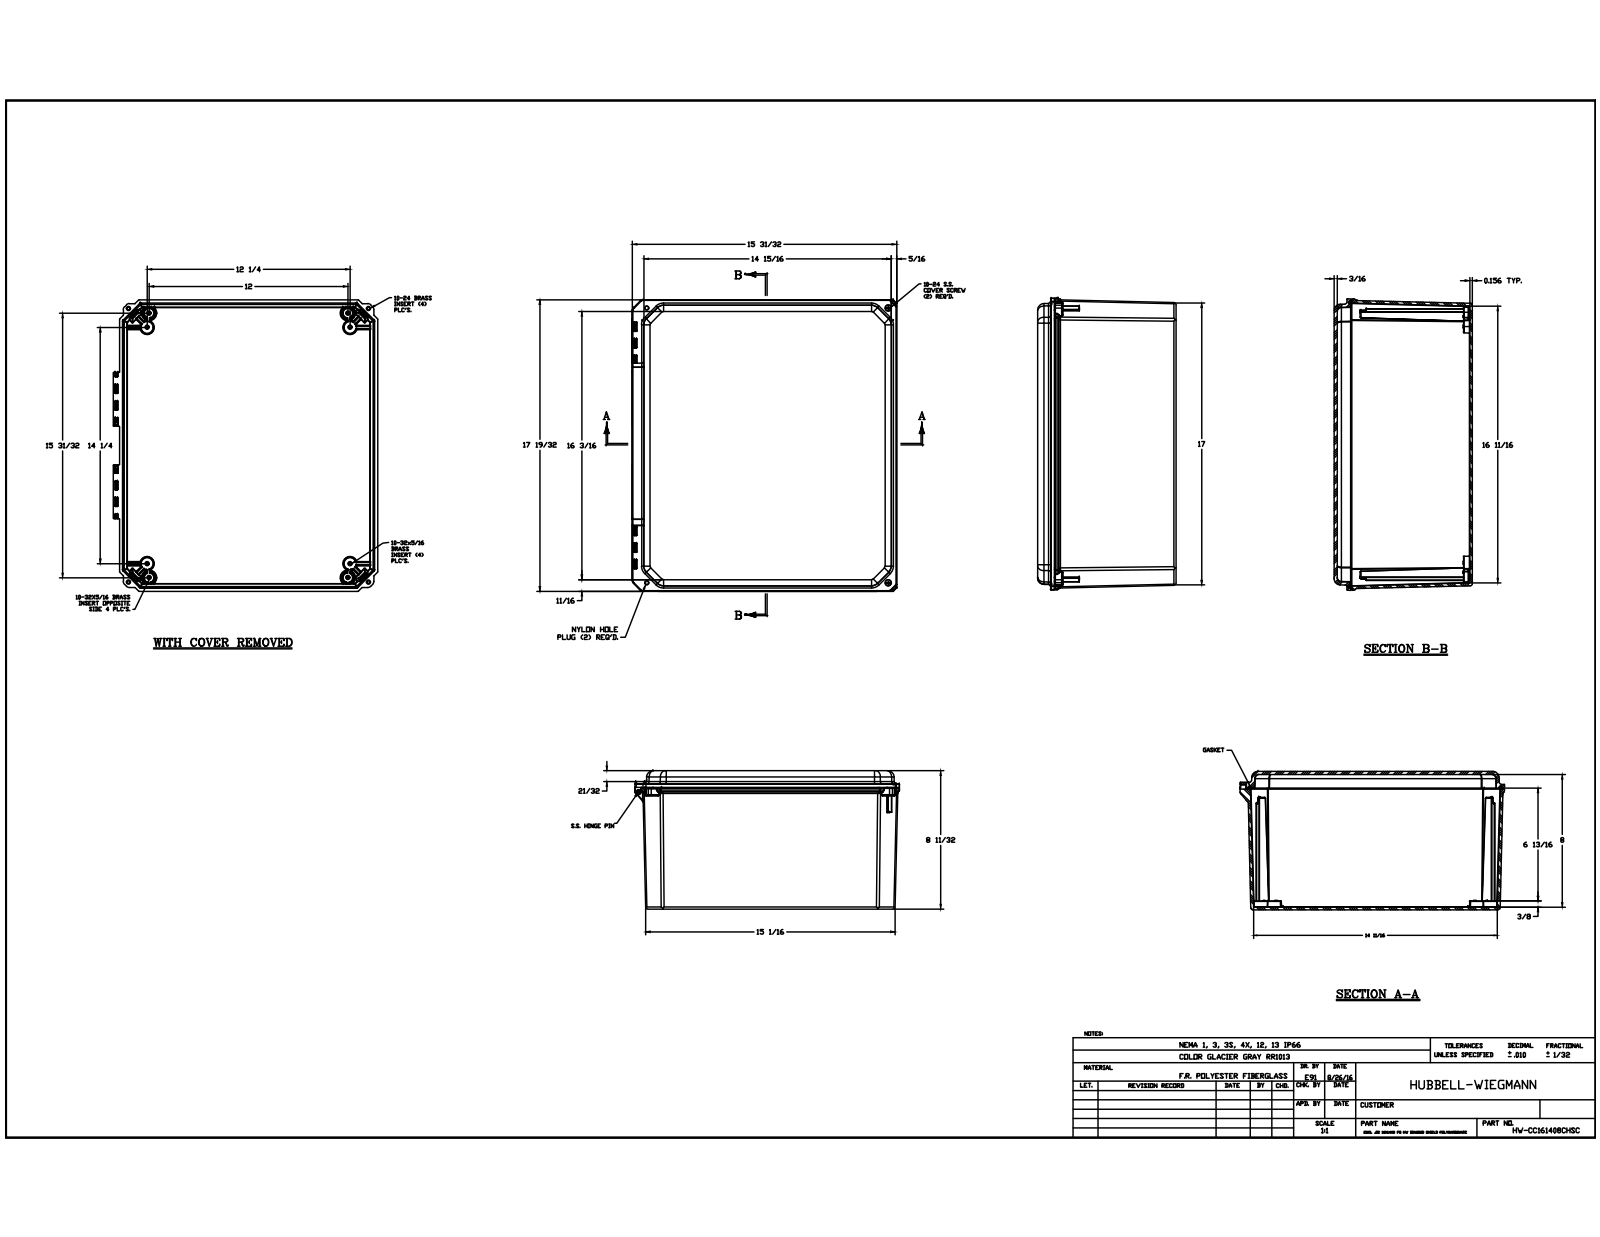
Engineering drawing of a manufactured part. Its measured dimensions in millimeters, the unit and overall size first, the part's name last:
Units: millimetres
Overall size (bounding box): 446.8 × 405.5 × 211.87
Round holes (diameter × count): ⌀3.96 ×12, ⌀3.86 ×8, ⌀5.56 ×4, ⌀6.4 ×4, ⌀7.92 ×4, ⌀3.48 ×2, ⌀3.81 ×2
Round bosses / shafts (diameter × count): ⌀6.25 ×12, ⌀11.43 ×2, ⌀5.3 ×2, ⌀5.05 ×2, ⌀3.43 ×1
Partial cylindrical surfaces — rounded edges, fillets, slot ends (radius × count): R0.25 ×202, R0.13 ×116, R0.51 ×59, R0.76 ×39, R3.17 ×29, R0.76 ×24, R2.29 ×24, R6.35 ×24
Main face-to-face distances: 3.18, 3.96, 208.69, 204.73, 211.87, 207.91, 4.56, 4.59, 184.94, 180.98
Hole centre spacings: 492.01, 21.97, 33.78, 41.94, 308.75, 311.15, 337.73, 342.11
Volume: 2 830 000 mm³ · Surface area: 1 408 000 mm²
Bodies: 23 solids, 2117 faces (592 planar, 800 cylindrical, 725 other)
Part name (STEP PRODUCT): HW-CC161408CHSC; DS161408BOX; BRASS INSERT-(; BRASS INSERT-(_1 (+7 more)
STEP written by: Autodesk Inventor 2017 (CONFIG_CONTROL_DESIGN)
